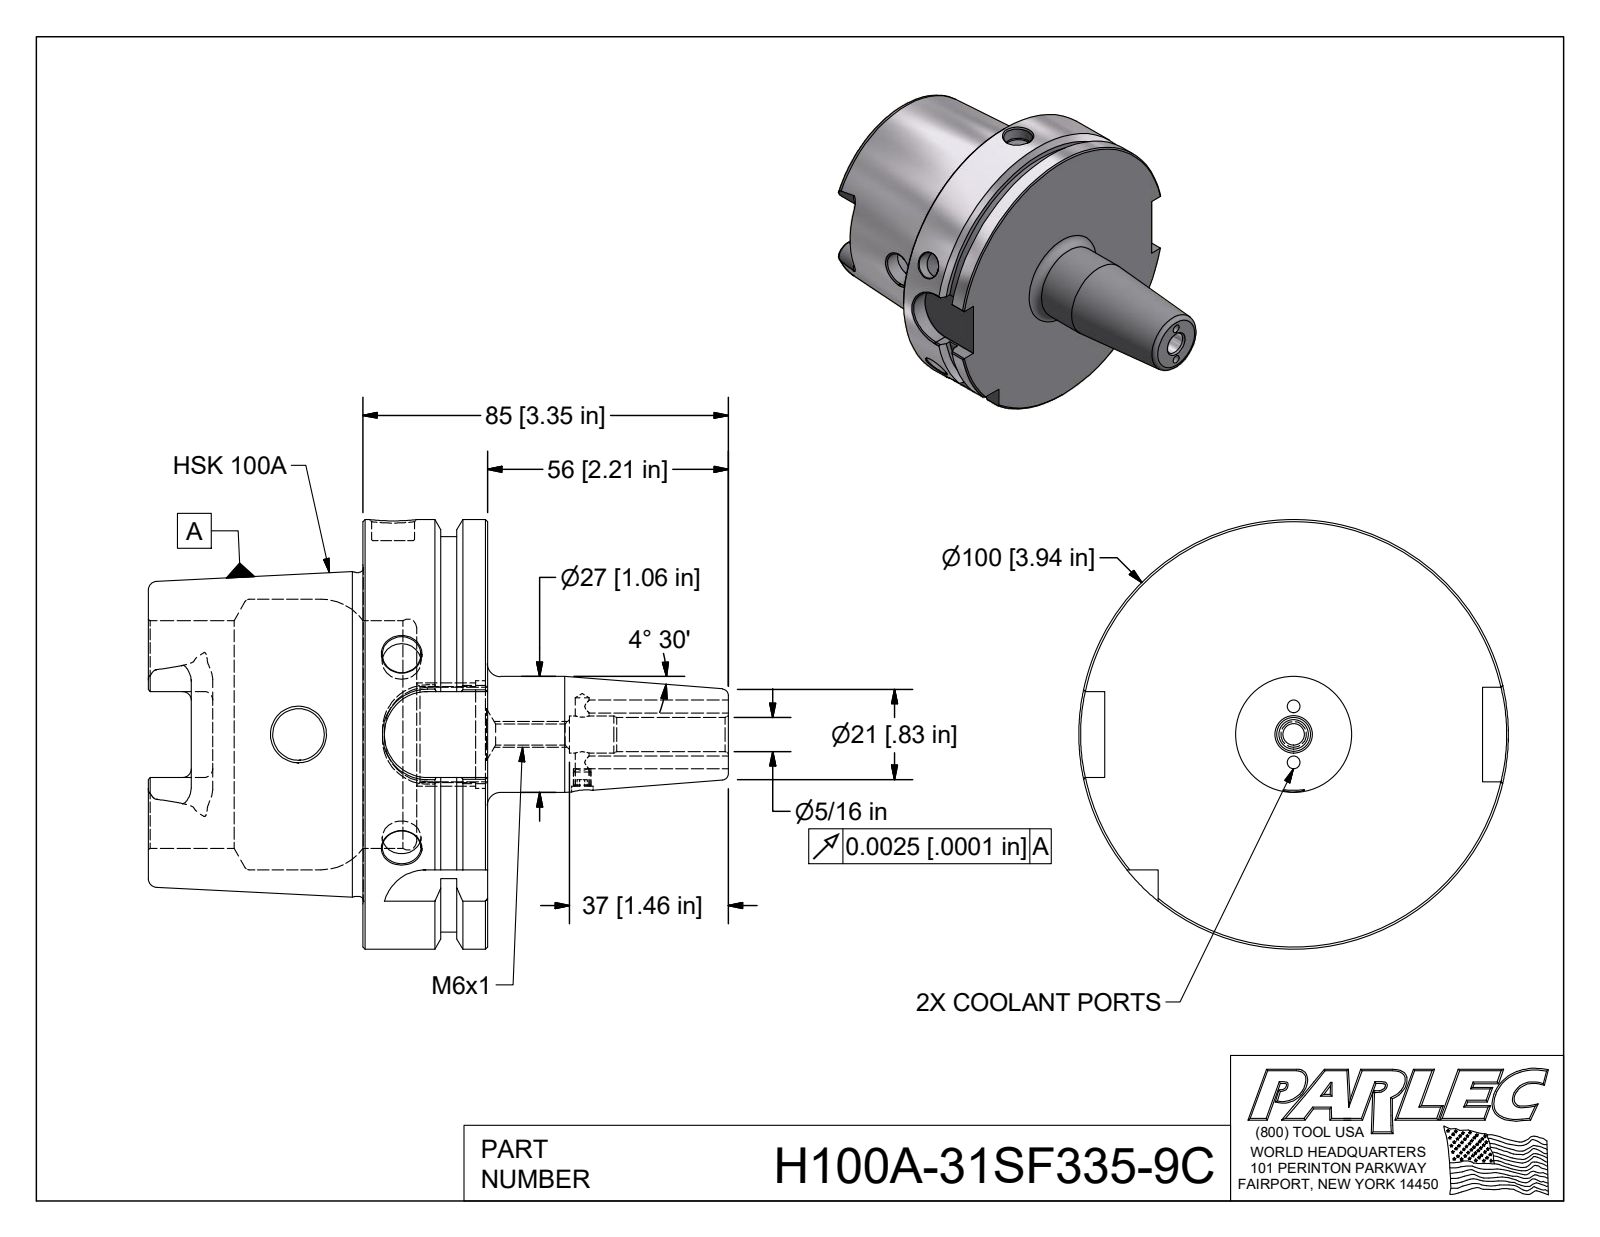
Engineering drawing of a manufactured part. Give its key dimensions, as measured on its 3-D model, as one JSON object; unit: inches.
{"step_written_by": "Autodesk Inventor 2018 (AUTOMOTIVE_DESIGN)", "units": "inches", "bodies": {"solids": 1, "faces": 149, "planar": 49, "cylindrical": 42, "other": 58}, "overall_size": [5.319, 3.937, 3.937], "volume_in3": 17.01, "surface_area_in2": 86.81, "round_holes": [[0.118, 2], [0.354, 2], [0.128, 1], [0.194, 1], [0.197, 1], [0.312, 1], [0.342, 1], [0.394, 1], [0.472, 1], [0.472, 1], [0.881, 1], [0.985, 1]], "round_bosses_or_shafts": [[3.937, 1], [3.622, 1], [2.967, 1], [1.063, 1]], "partial_cylinders_radius": [[0.079, 6], [0.192, 4], [0.394, 4]], "face_to_face_distances": [1.142, 0.492, 0.65, 1.969, 2.461, 3.11, 3.465, 0.861, 2.83, 0.369], "hole_center_spacings": [0.256, 0.512, 1.734]}
